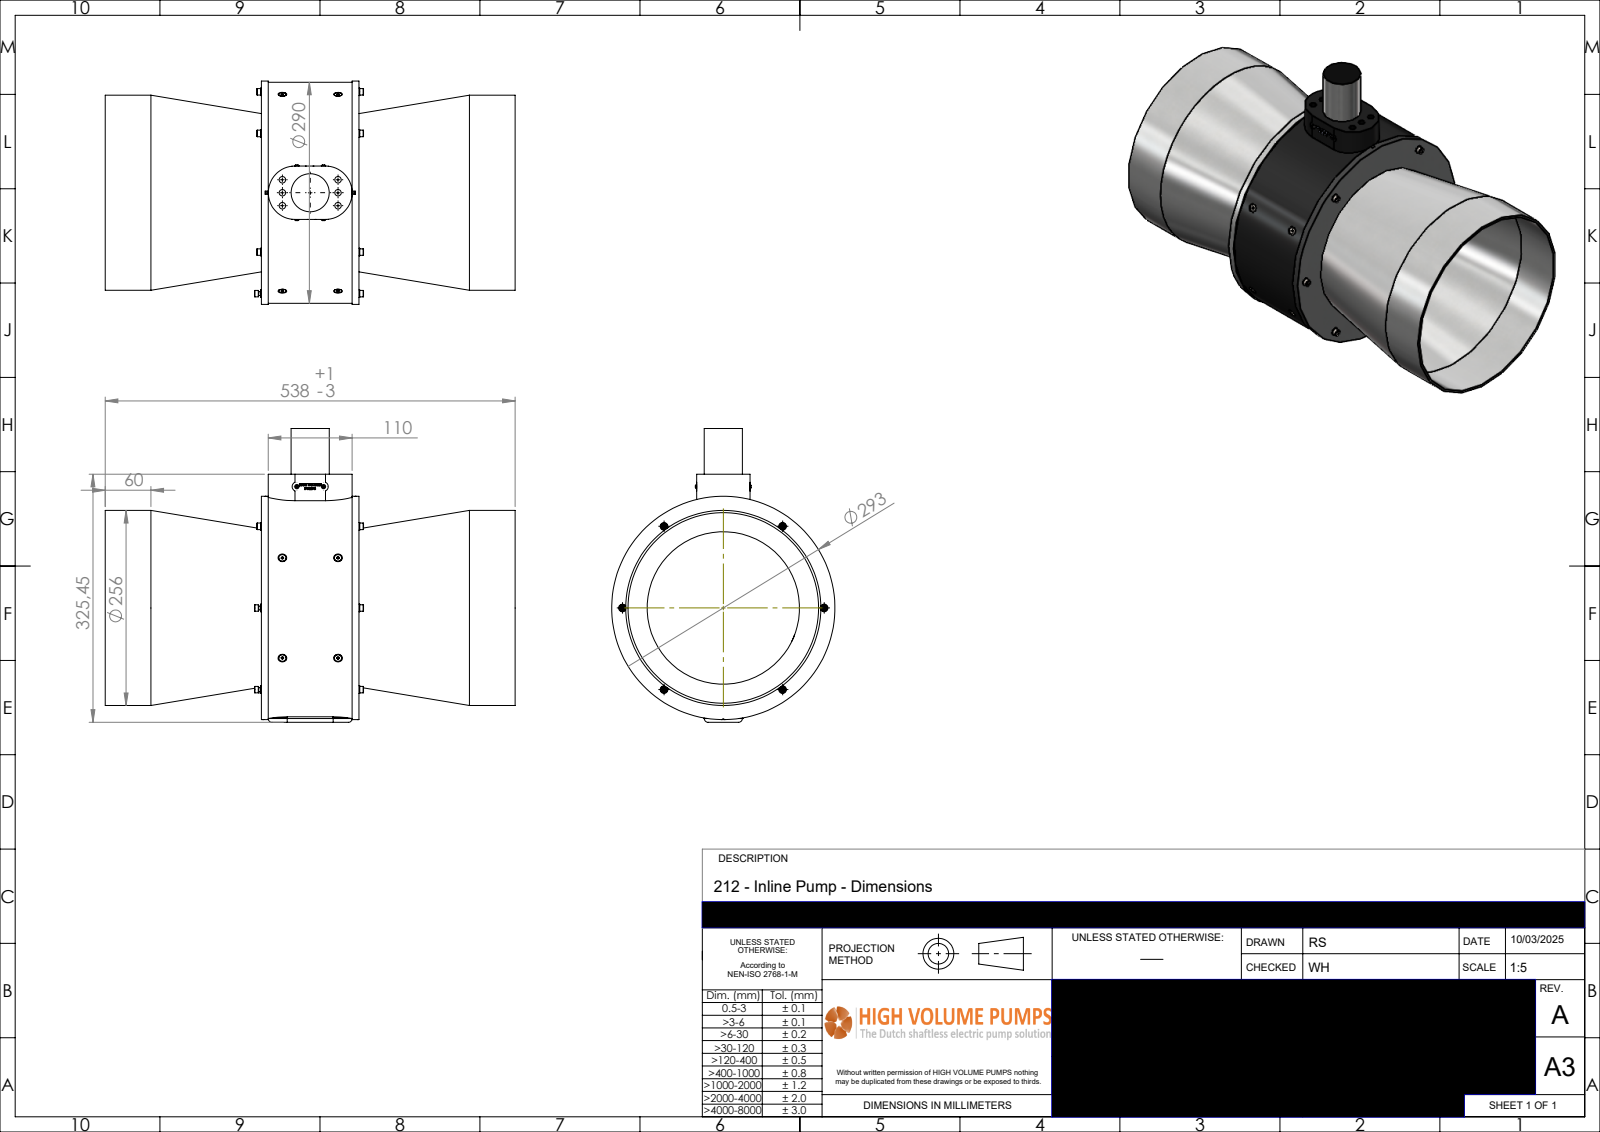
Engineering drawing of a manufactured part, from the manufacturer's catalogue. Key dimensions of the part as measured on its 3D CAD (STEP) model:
Part name (STEP PRODUCT): P-212-030-rev-A-IP
STEP written by: SolidWorks 2024 (AUTOMOTIVE_DESIGN)
Units: millimetres
Bodies: 1 solid, 1006 faces (671 planar, 133 cylindrical, 202 other)
Overall size (bounding box): 538.06 × 385.45 × 293
Volume: 5 455 000 mm³ · Surface area: 927 334 mm²
Round holes (diameter × count): ⌀5.6 ×6, ⌀8.5 ×6, ⌀5.5 ×4, ⌀207 ×1, ⌀250 ×1
Round bosses / shafts (diameter × count): ⌀10 ×6, ⌀9.64 ×6, ⌀8.5 ×6, ⌀5 ×6, ⌀5.7 ×2, ⌀293 ×1, ⌀290 ×1, ⌀256 ×1
Partial cylindrical surfaces — rounded edges, fillets, slot ends (radius × count): R2 ×4, R25 ×4, R1 ×2, R5 ×2, R6.25 ×2, R35 ×2, R142 ×1
Main face-to-face distances: 128.06, 205, 333.06, 5, 123.06, 210, 328.06, 325.45, 9, 4
Hole centre spacings: 73, 17, 74.95, 132.37, 132.38, 264.75, 34, 80.53
